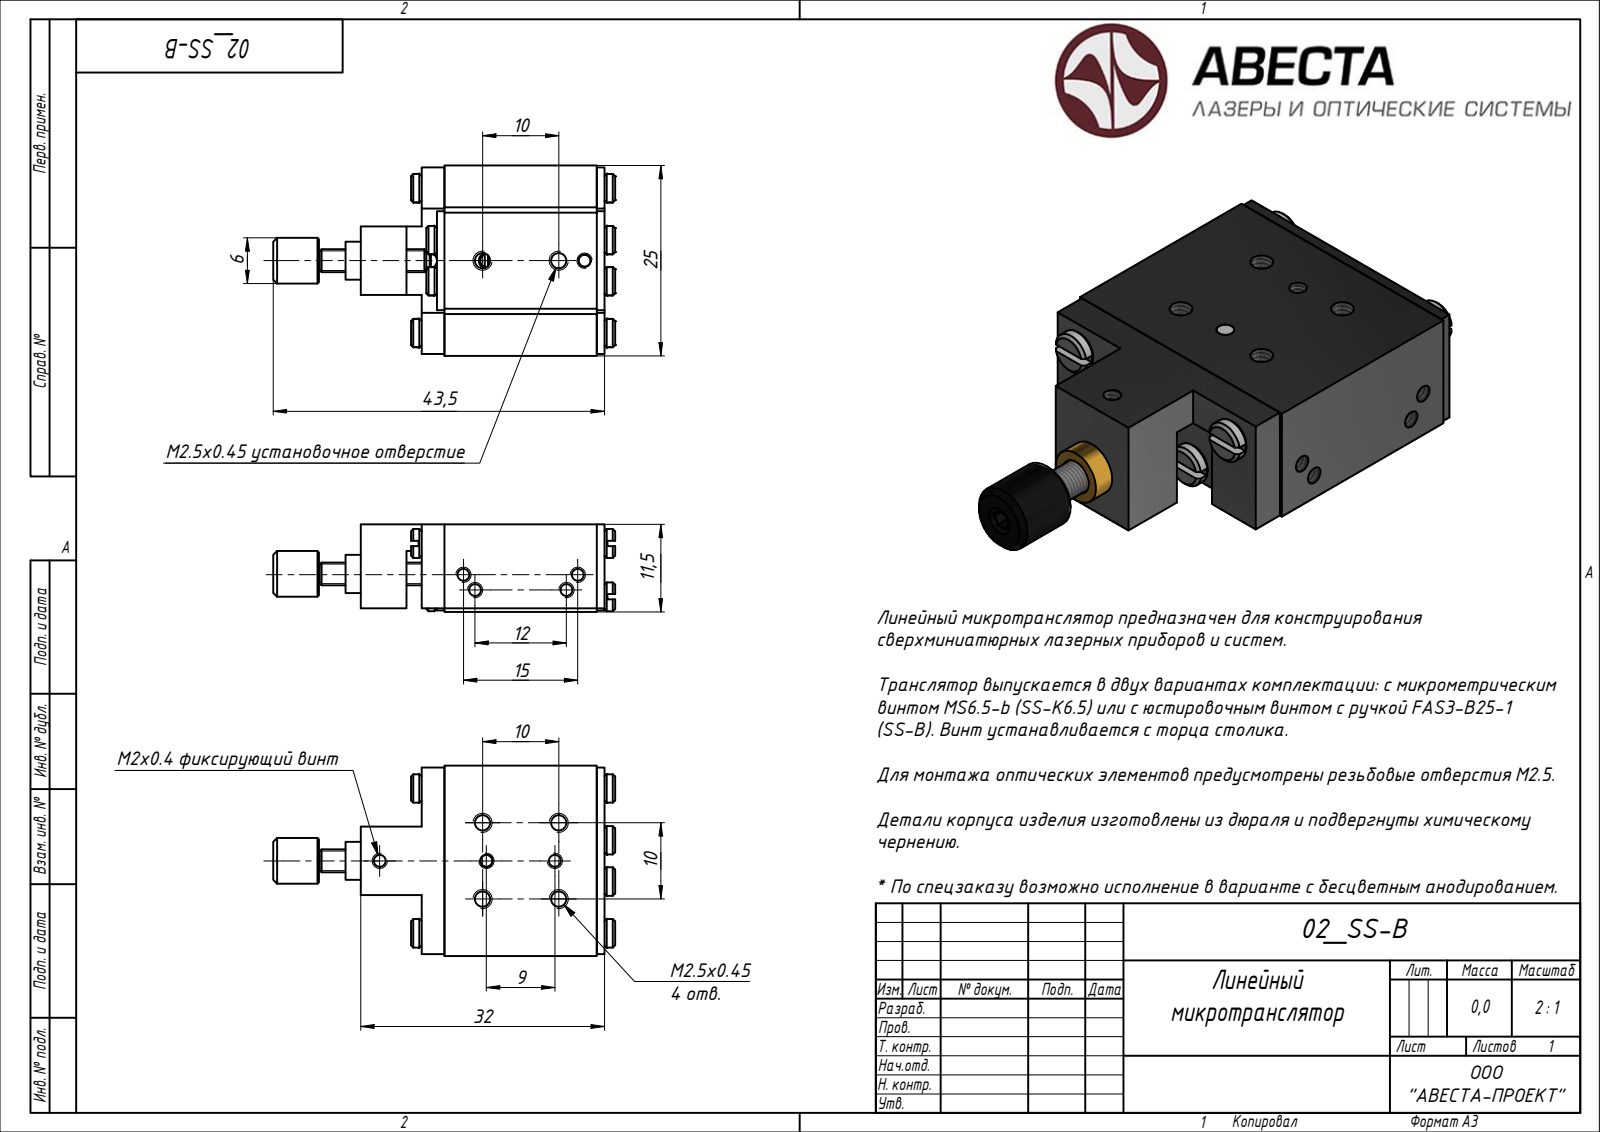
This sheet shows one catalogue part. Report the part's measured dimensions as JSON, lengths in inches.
{"step_written_by": "Rhino 7.34 (AUTOMOTIVE_DESIGN)", "units": "inches", "bodies": {"solids": 2, "faces": 337, "planar": 158, "cylindrical": 91, "other": 88}, "overall_size": [1.767, 0.984, 0.453], "volume_in3": 0.38, "surface_area_in2": 9.106, "round_holes": [[0.062, 7], [0.079, 6], [0.062, 1], [0.079, 1], [0.157, 1]], "round_bosses_or_shafts": [[0.079, 6], [0.15, 4], [0.059, 2], [0.236, 1], [0.197, 1], [0.118, 1], [0.098, 1], [0.096, 1]], "partial_cylinders_radius": [[0.059, 4], [0.031, 1], [0.031, 1]], "face_to_face_distances": [0.433, 0.043, 0.224, 0.453, 0.02, 0.315, 0.244, 0.283, 0.984, 0.15], "hole_center_spacings": [0.394, 0.197, 0.44, 0.098, 0.198, 0.238, 0.423, 0.537]}
